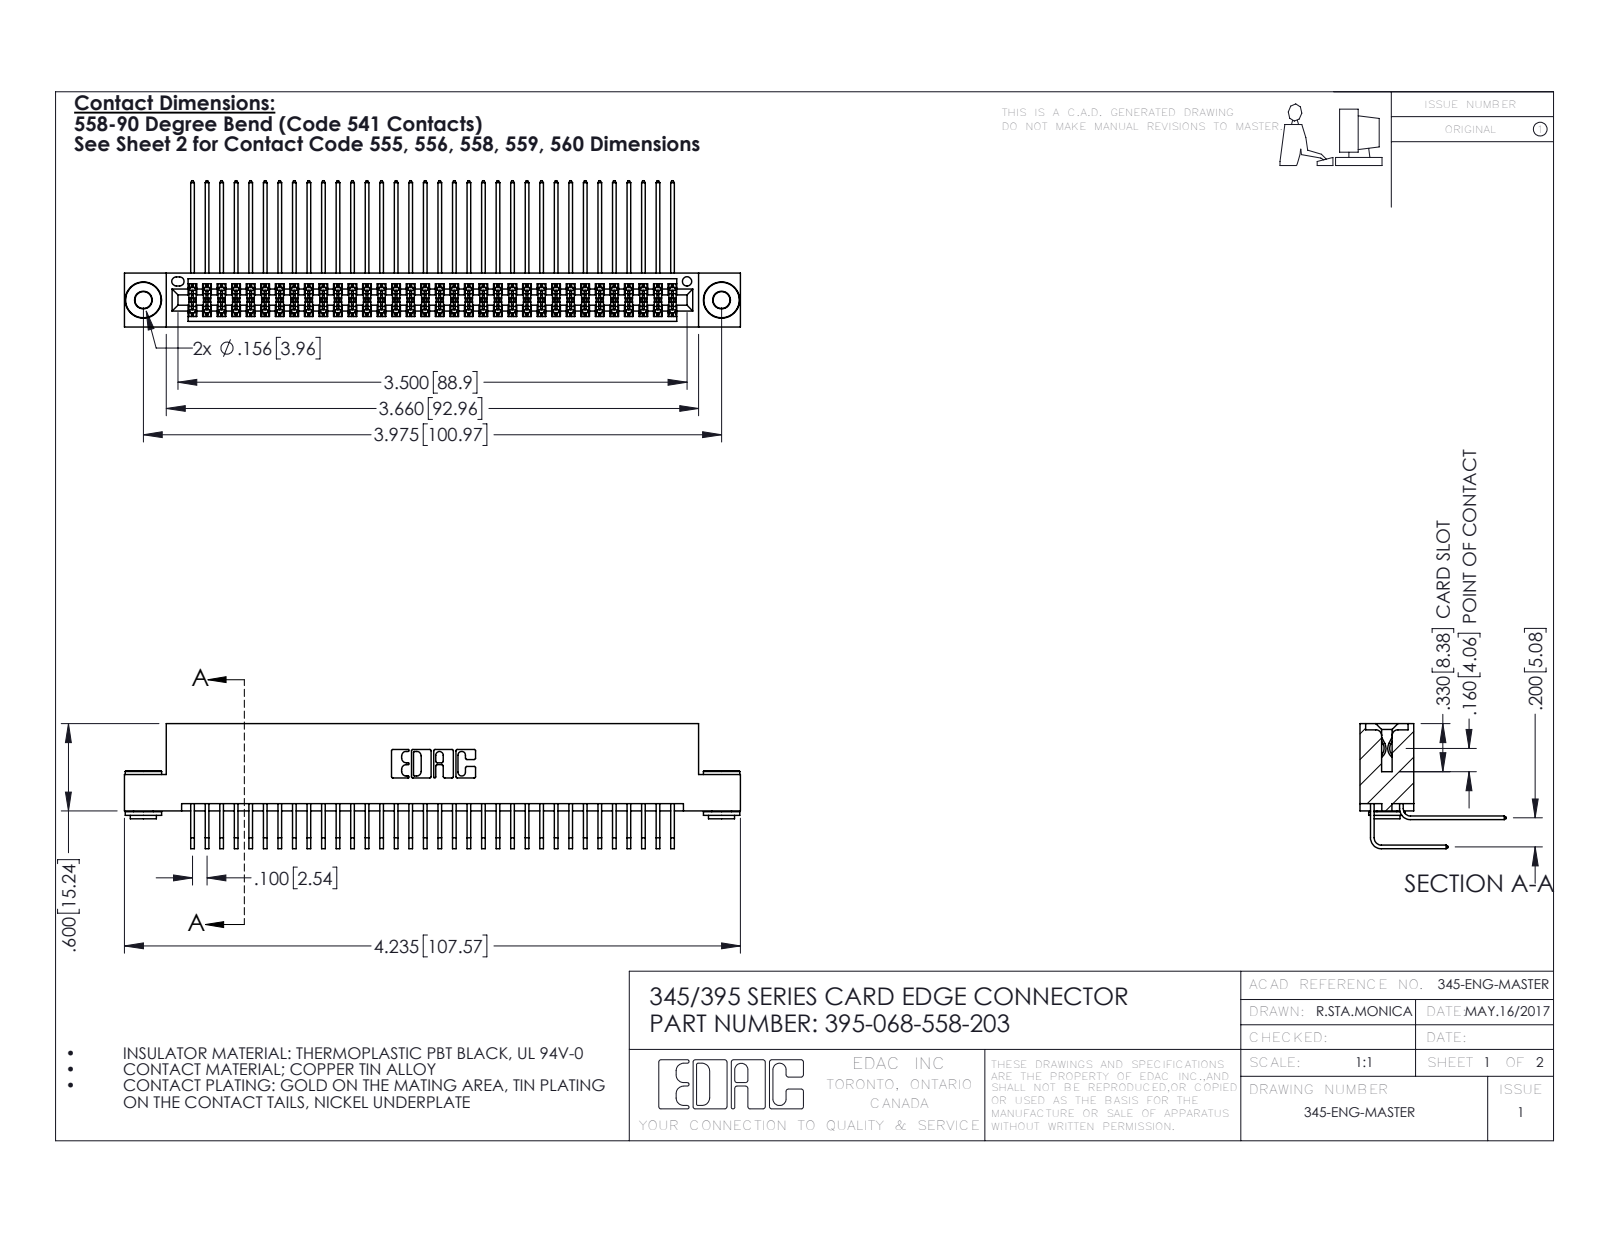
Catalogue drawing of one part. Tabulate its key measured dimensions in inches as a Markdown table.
| quantity | value |
| --- | --- |
| part name | 345-292-001_558 559 Tail - 1; 345-250-002_345-250-002-102; 345-292-001_558 Tail - 2; 395-068-558-203 (+1 more) |
| STEP written by | SolidWorks 2016 (CONFIG_CONTROL_DESIGN) |
| units | inches |
| bodies | 71 solids, 3700 faces (2470 planar, 1222 cylindrical, 8 other) |
| overall size | 4.235 × 1.005 × 0.859 |
| volume | 0.658 in³ |
| surface area | 27.65 in² |
| round holes (diameter × count) | 0.116 × 2, 0.156 × 2, 0.064 × 1 |
| round bosses / shafts (diameter × count) | 0.25 × 2, 0.18 × 2, 0.136 × 2 |
| partial cylindrical surfaces (radius × count) | 0.006 × 103, 0.01 × 22, 0.007 × 6, 0.031 × 6, 0.026 × 3, 0.014 × 2, 0.019 × 2, 0.022 × 2 |
| main face-to-face distances | 0.2, 0.072, 0.298, 0.37, 0.025, 0.098, 0.272, 0.225, 0.025, 0.285 |
| hole center spacings | 0.27, 3.74, 3.975 |
